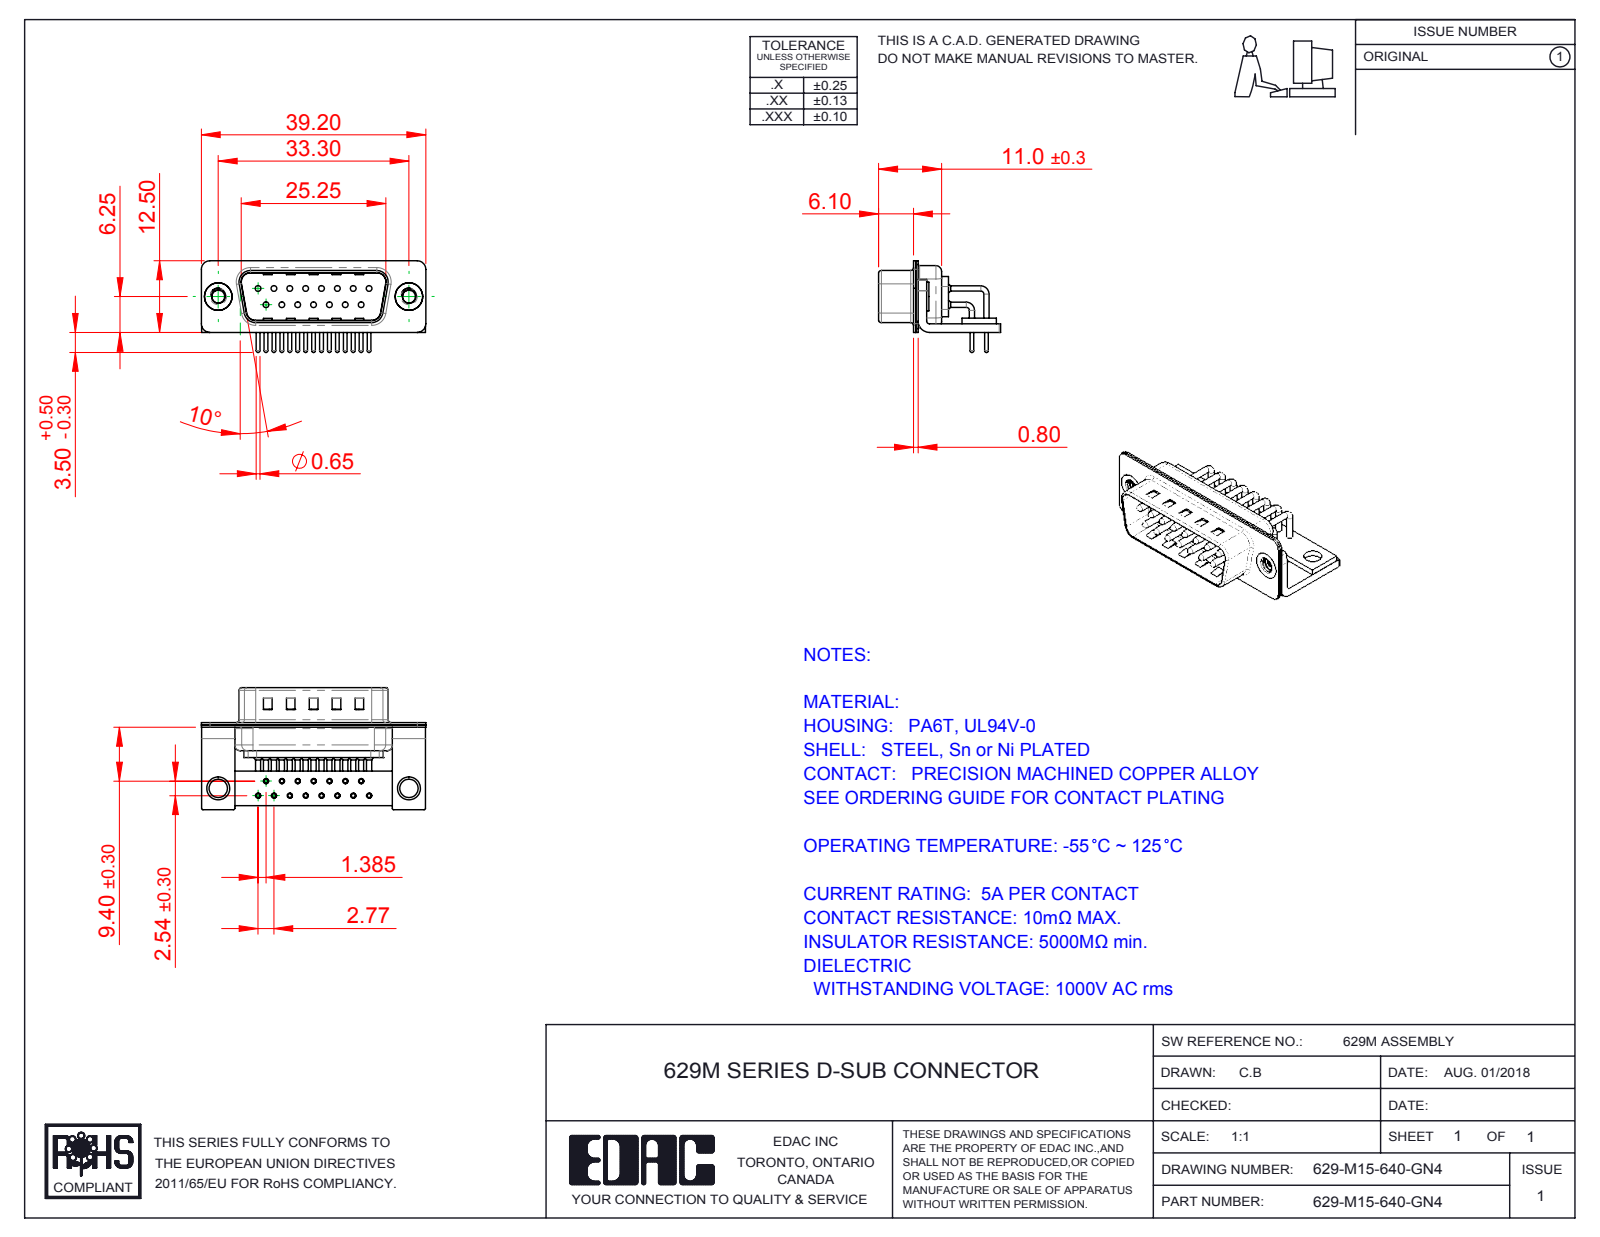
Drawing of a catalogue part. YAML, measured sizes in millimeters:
part_name: "629M Housing_15 Contacts; 629M Shell Rear_15 Contacts; 629M Contact Row 1; 629M Shell Front_15 Contacts (+5 more)"
step_written_by: "SolidWorks 2016 (CONFIG_CONTROL_DESIGN)"
units: millimeters
bodies: {solids: 23, faces: 2070, planar: 1125, cylindrical: 725, other: 220}
overall_size: [39.2, 21.3, 16]
volume: 2435
surface_area: 6519
round_holes:
  - {diameter: 0.9, count: 15}
  - {diameter: 1, count: 15}
  - {diameter: 1.7, count: 15}
  - {diameter: 2, count: 15}
  - {diameter: 2.26, count: 2}
  - {diameter: 3.2, count: 2}
  - {diameter: 4, count: 2}
  - {diameter: 4.8, count: 2}
round_bosses_or_shafts:
  - {diameter: 0.9, count: 21}
  - {diameter: 1.5, count: 15}
  - {diameter: 0.65, count: 15}
  - {diameter: 5, count: 2}
  - {diameter: 4.9, count: 2}
partial_cylinders:
  - {radius: 0.25, count: 16}
  - {radius: 1.5, count: 16}
  - {radius: 1.01, count: 15}
  - {radius: 2, count: 13}
  - {radius: 0.5, count: 9}
  - {radius: 1.6, count: 8}
  - {radius: 0.6, count: 4}
  - {radius: 0.65, count: 4}
face_to_face_distances: [0.4, 1.5, 0.85, 0.8, 1.25, 10.4, 9.55, 1.9, 1, 8.3]
hole_center_spacings: [2.77, 5.54, 3.16, 8.31, 4.87, 11.08, 2.89, 7.37]
